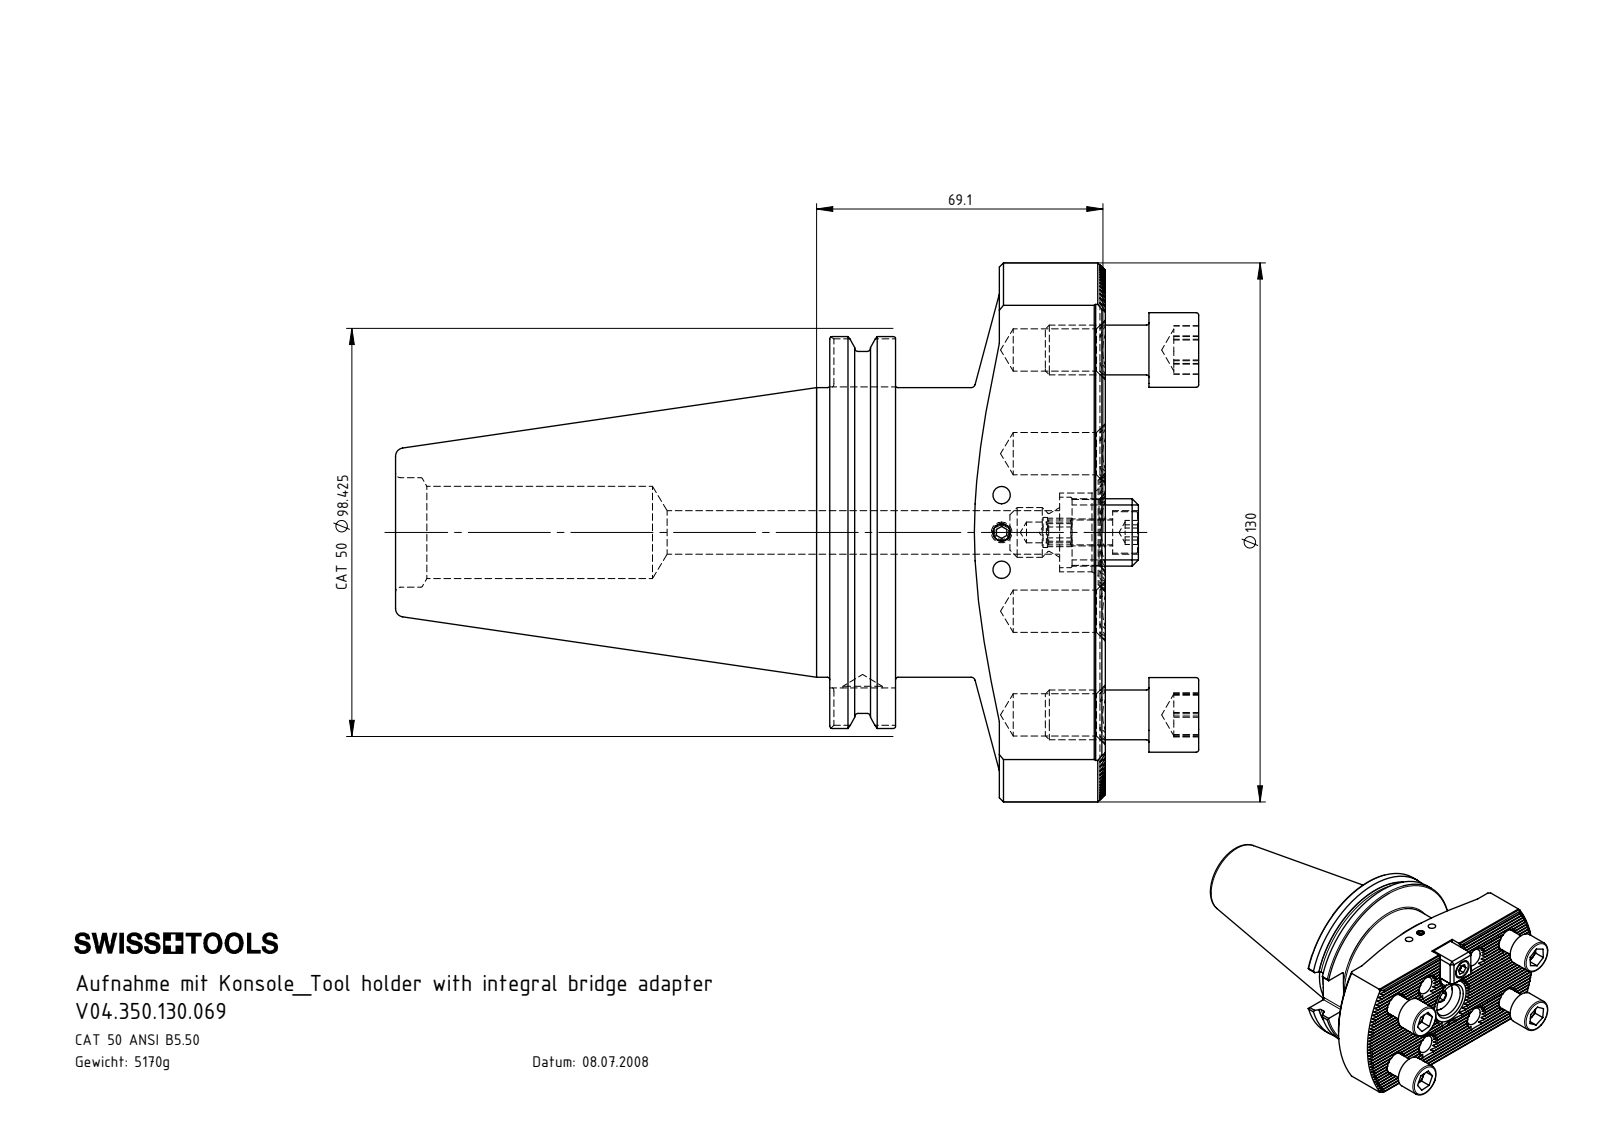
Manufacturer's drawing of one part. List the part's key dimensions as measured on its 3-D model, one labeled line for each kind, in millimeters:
Part name (STEP PRODUCT): DIN 908 - M12x1.5; ISO 4026 - M5 x 8; ISO 4762 - M12 x 25; ISO 4762 - M6 x 16 (+3 more)
STEP written by: SolidWorks 2017 (AUTOMOTIVE_DESIGN)
Units: millimetres
Bodies: 10 solids, 749 faces (495 planar, 161 cylindrical, 93 other)
Overall size (bounding box): 193.8 × 130 × 98.42
Volume: 658 596 mm³ · Surface area: 92 514 mm²
Round holes (diameter × count): ⌀10.2 ×8, ⌀4.2 ×3, ⌀10.5 ×2, ⌀5 ×1, ⌀6.5 ×1, ⌀7.24 ×1, ⌀9.5 ×1, ⌀19 ×1, ⌀22.25 ×1, ⌀26.4 ×1
Round bosses / shafts (diameter × count): ⌀12 ×5, ⌀18 ×4, ⌀98.42 ×1, ⌀91 ×1, ⌀69.85 ×1, ⌀17 ×1, ⌀10 ×1, ⌀6 ×1
Partial cylindrical surfaces — rounded edges, fillets, slot ends (radius × count): R0.14 ×34, R0.8 ×8, R7.95 ×1, R65 ×1
Main face-to-face distances: 1.73, 17.32, 15.87, 70, 8.66, 3.46, 5.2, 6.93, 15.59, 19.05
Hole centre spacings: 25, 27.59, 40, 47.17, 48.33, 63, 74.63, 9
